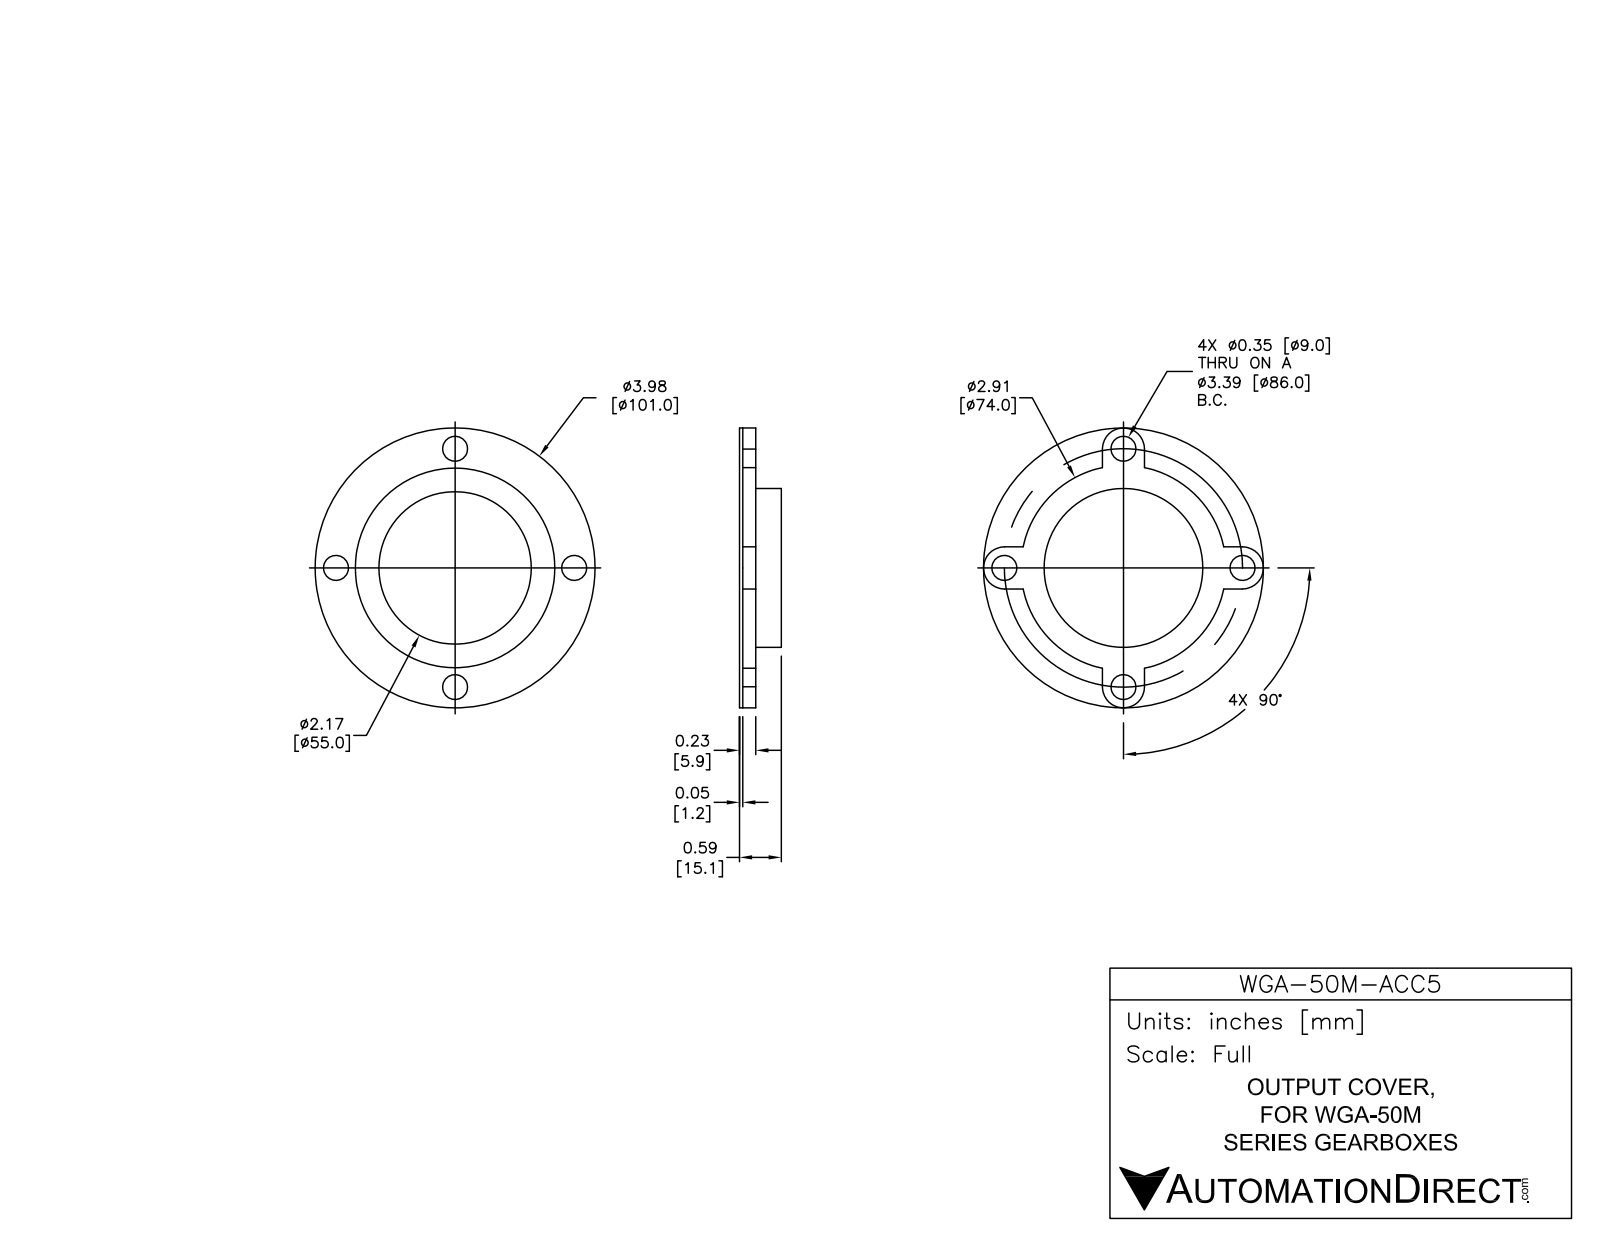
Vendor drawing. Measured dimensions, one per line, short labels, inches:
name: WGA-50M-ACC5
written by: SolidWorks 2014 (AUTOMOTIVE_DESIGN)
unit: in
bodies: 1 solid, 42 faces (17 planar, 25 cylindrical, 0 other)
size: 3.976 × 3.976 × 0.594
volume: 0.872 in³; area: 34.71 in²
holes: 4× ⌀0.354, 1× ⌀2.165, 1× ⌀2.835
bosses: 1× ⌀3.976, 1× ⌀2.256
rounds: 4× R0.299, 1× R1.457
face distances: 0.047, 0.185, 0.547, 0.594, 0.043, 0.504, 0.551, 0.362, 0.319, 0.232
hole spacings: 1.693, 2.394, 3.386
